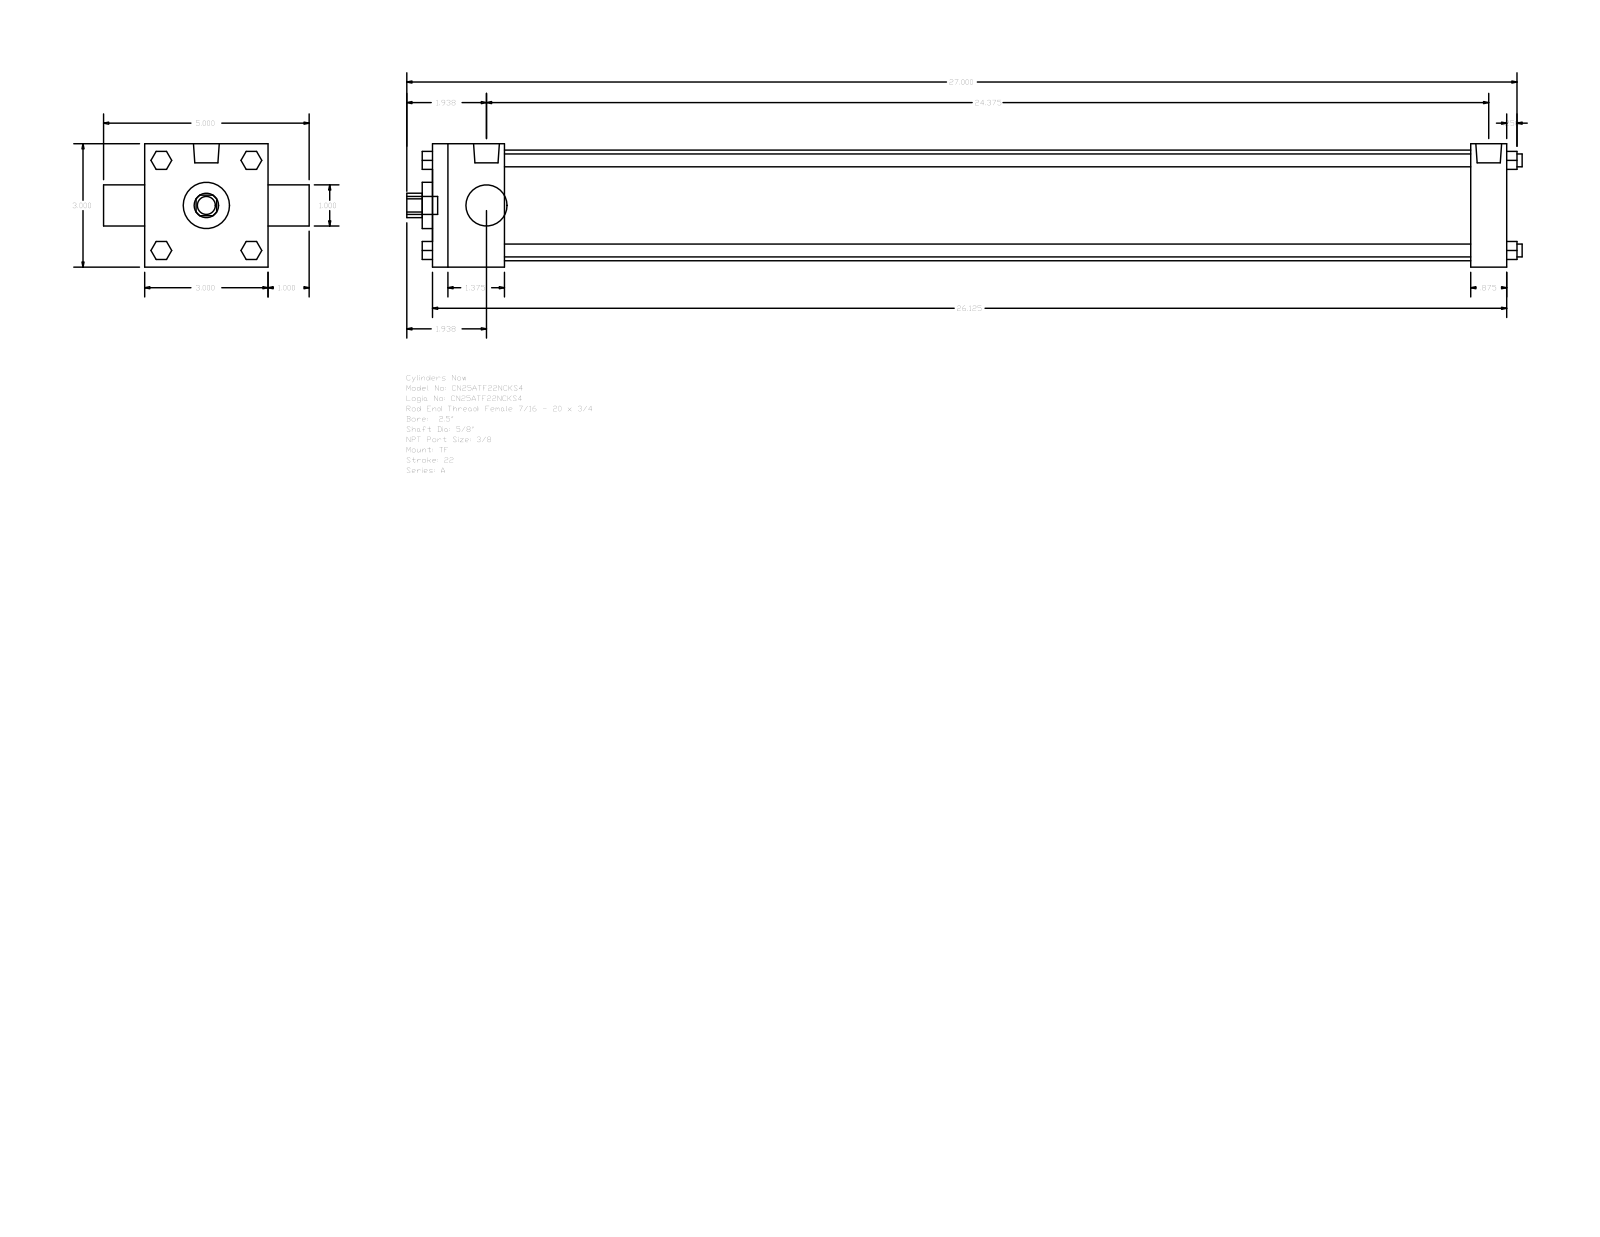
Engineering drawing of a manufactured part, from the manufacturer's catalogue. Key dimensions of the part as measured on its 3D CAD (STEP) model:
Part name (STEP PRODUCT): A_TF__0250_0.625
STEP written by: GSSL Pune (CONFIG_CONTROL_DESIGN)
Units: millimetres
Bodies: 0 solids, 120 faces (92 planar, 28 cylindrical, 0 other)
Overall size (bounding box): 688.98 × 127 × 76.2
Round holes (diameter × count): ⌀15.88 ×1, ⌀25.4 ×1, ⌀28.57 ×1, ⌀68.33 ×1
Round bosses / shafts (diameter × count): ⌀7.94 ×4, ⌀5.56 ×3, ⌀15.93 ×2, ⌀11.11 ×1
Partial cylindrical surfaces — rounded edges, fillets, slot ends (radius × count): R7.54 ×1
Main face-to-face distances: 76.2, 663.57, 44.45, 641.35, 596.9, 619.12, 22.22, 25.4, 101.6, 6.35
